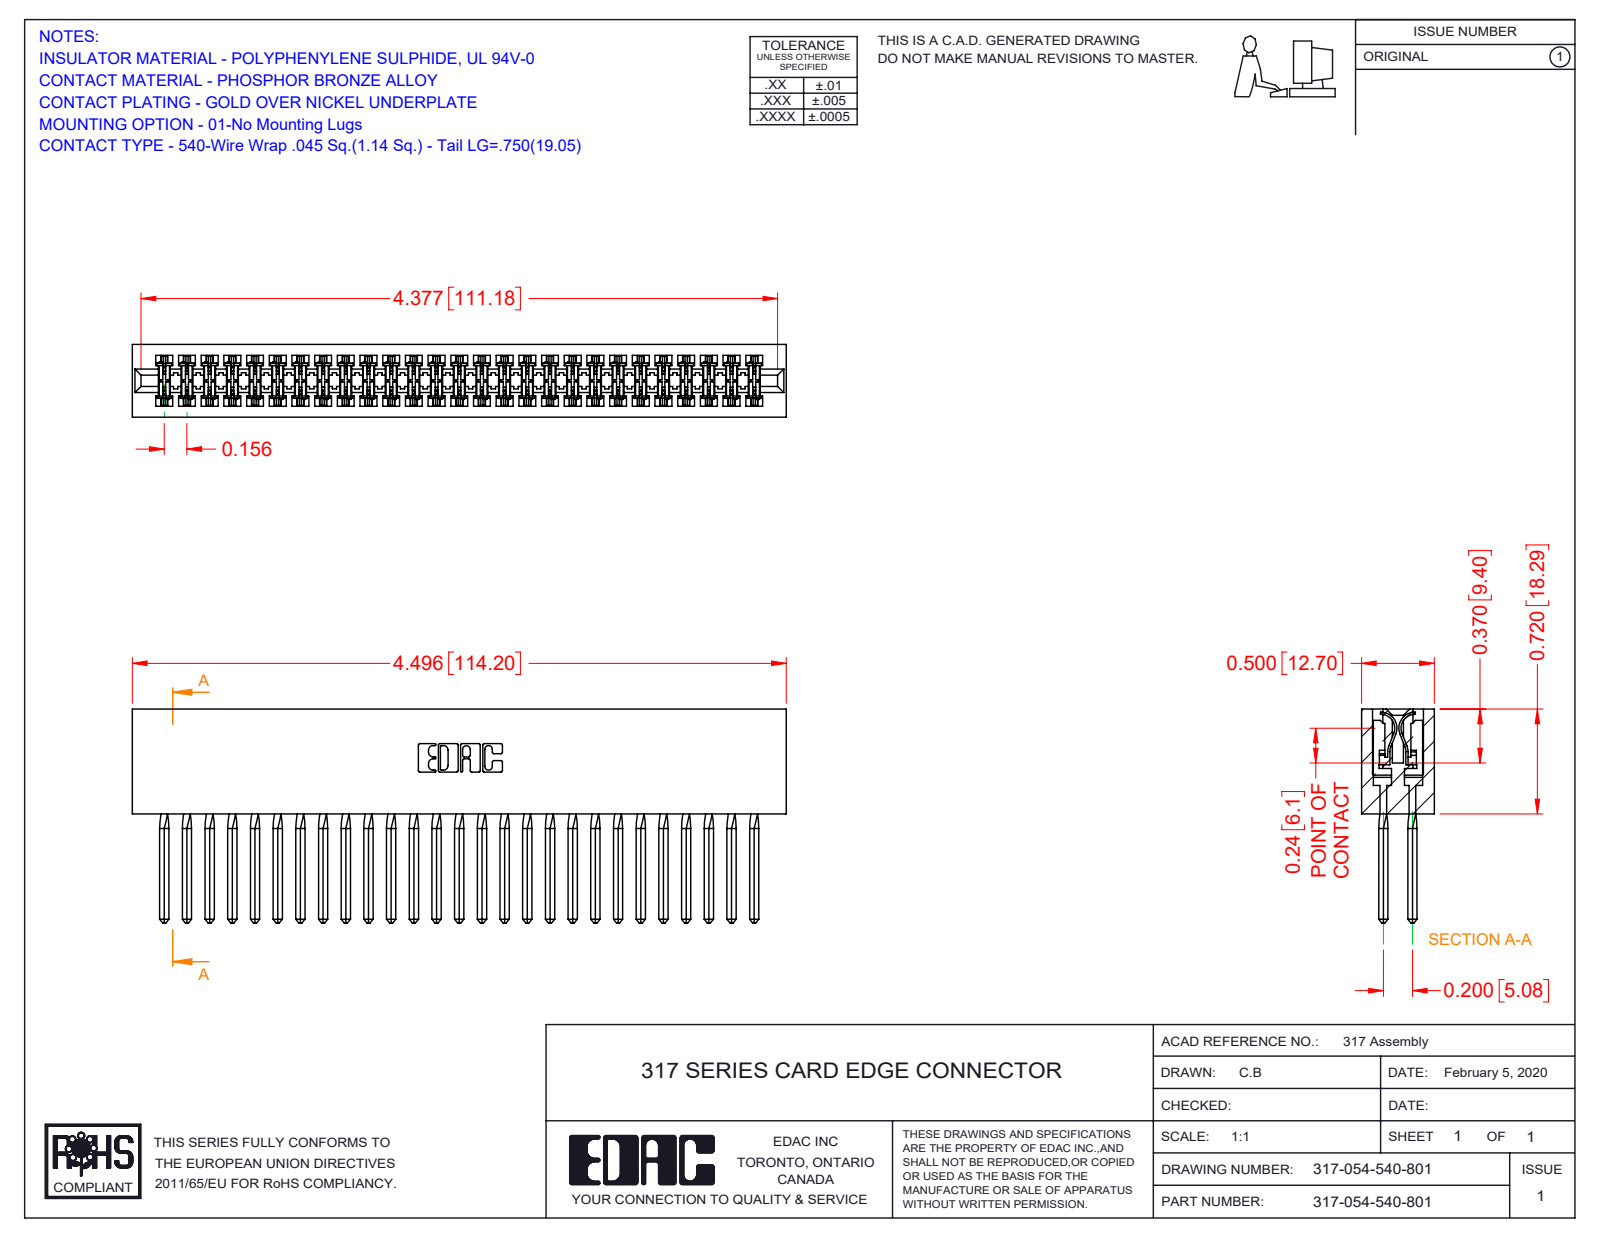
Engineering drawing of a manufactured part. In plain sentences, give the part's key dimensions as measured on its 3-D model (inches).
The part is named "317 Part_Lugless; 317-054-540-801; 317-290-001_540". Its 3-D file was written by "SolidWorks 2016 (CONFIG_CONTROL_DESIGN)". It is 55 solids with 4896 faces: 3992 planar, 688 cylindrical and 216 other. Overall it measures 4.496 by 1.47 by 0.5 inches. Its volume is 1.248 cubic inches and its surface area 46.78 square inches. Partial cylindrical surfaces (rounded edges, fillets, slot ends): 108 of radius 0.015, 22 of radius 0.01, 6 of radius 0.007, 6 of radius 0.031, 3 of radius 0.026, 2 of radius 0.095, 2 of radius 0.1, 2 of radius 0.11. The main face-to-face distances are 0.075, 0.5, 0.425, 0.35, 0.11, 0.195, 0.094, 0.72, 0.2, 0.115.
